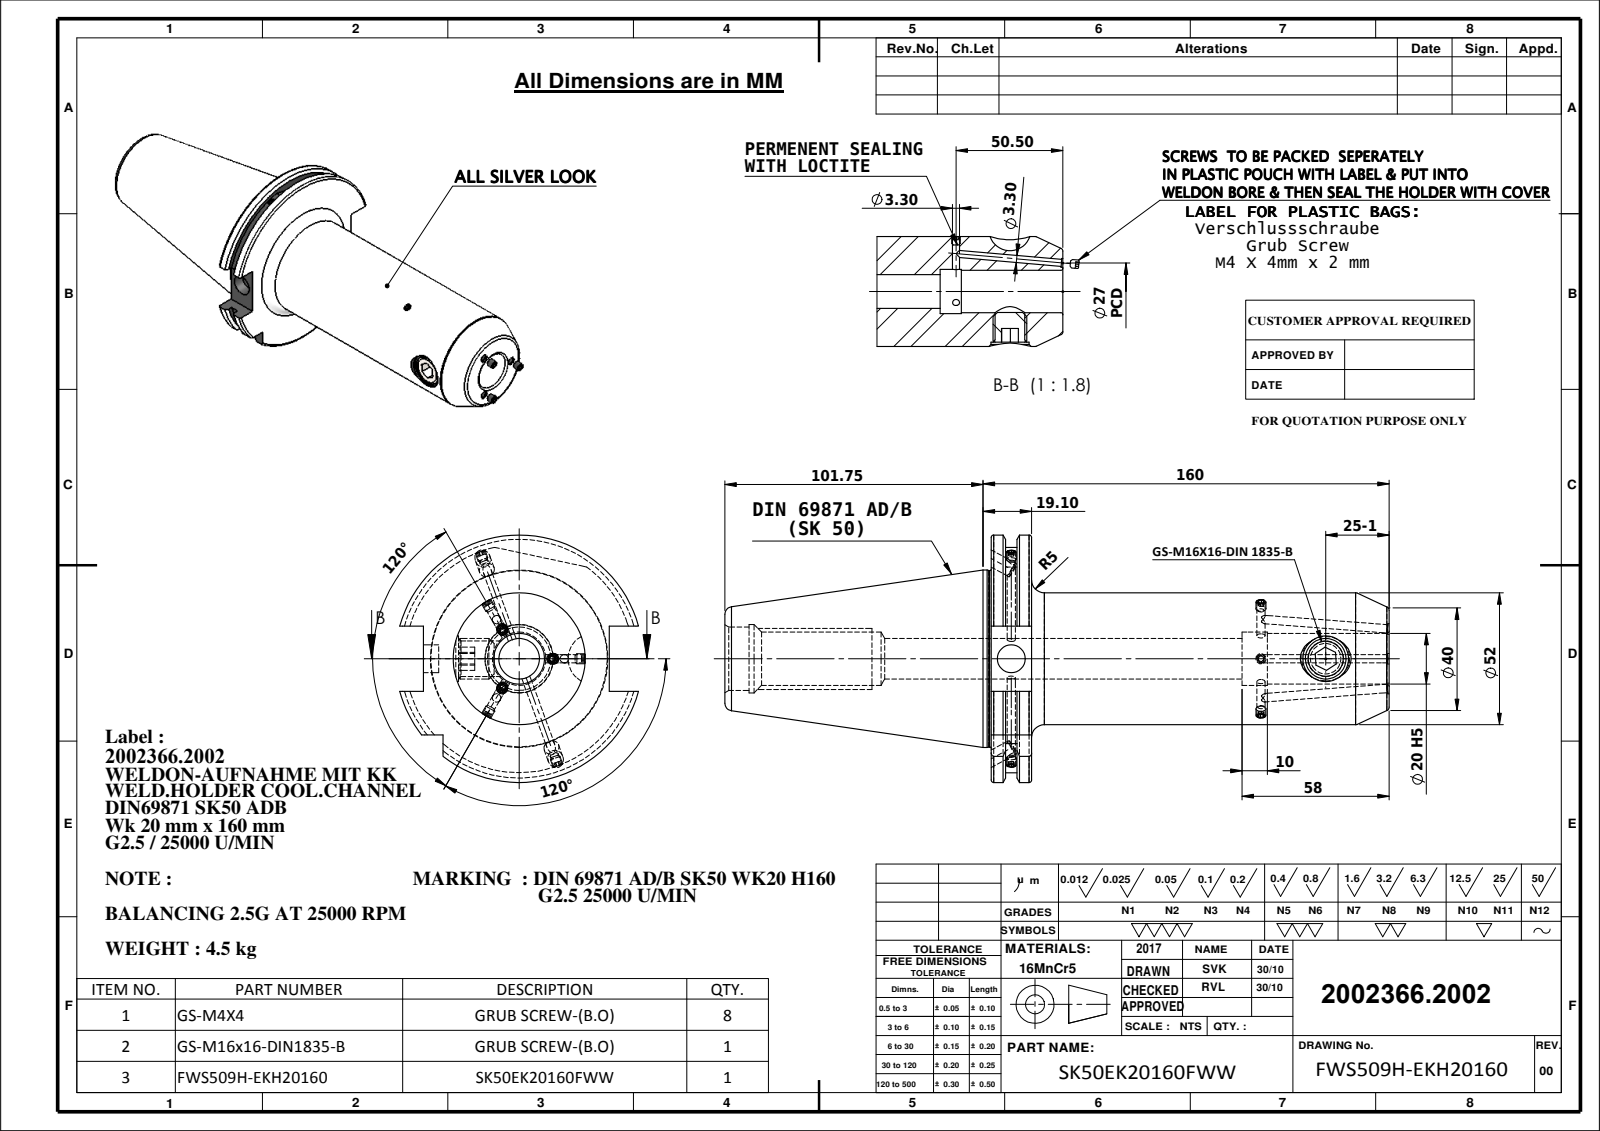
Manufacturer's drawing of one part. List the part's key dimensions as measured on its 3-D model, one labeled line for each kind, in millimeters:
Part name (STEP PRODUCT): M16X16_ISO 4026 - M16 x 10-N; Copy of M4X4_DIN 913 - M4 x 4-N; 91506-WK220160; SK50EK20160FWW
STEP written by: SolidWorks 2009 (CONFIG_CONTROL_DESIGN)
Units: millimetres
Bodies: 10 solids, 285 faces (116 planar, 85 cylindrical, 84 other)
Overall size (bounding box): 269.43 × 97.5 × 94.05
Volume: 582 576 mm³ · Surface area: 78 025 mm²
Round holes (diameter × count): ⌀3.3 ×7, ⌀4.2 ×3, ⌀6 ×2, ⌀11 ×1, ⌀14 ×1, ⌀16 ×1, ⌀18 ×1, ⌀20 ×1, ⌀21 ×1, ⌀25 ×1, ⌀27 ×1
Round bosses / shafts (diameter × count): ⌀4 ×8, ⌀69.85 ×1, ⌀69.45 ×1, ⌀52 ×1, ⌀16 ×1
Partial cylindrical surfaces — rounded edges, fillets, slot ends (radius × count): R44.9 ×1, R48.75 ×1
Main face-to-face distances: 15.9, 156.8, 140.9, 5.66, 10.24, 151.14, 10.15, 4.49, 5.75, 146.65
Hole centre spacings: 25.5, 98.4, 123.9
